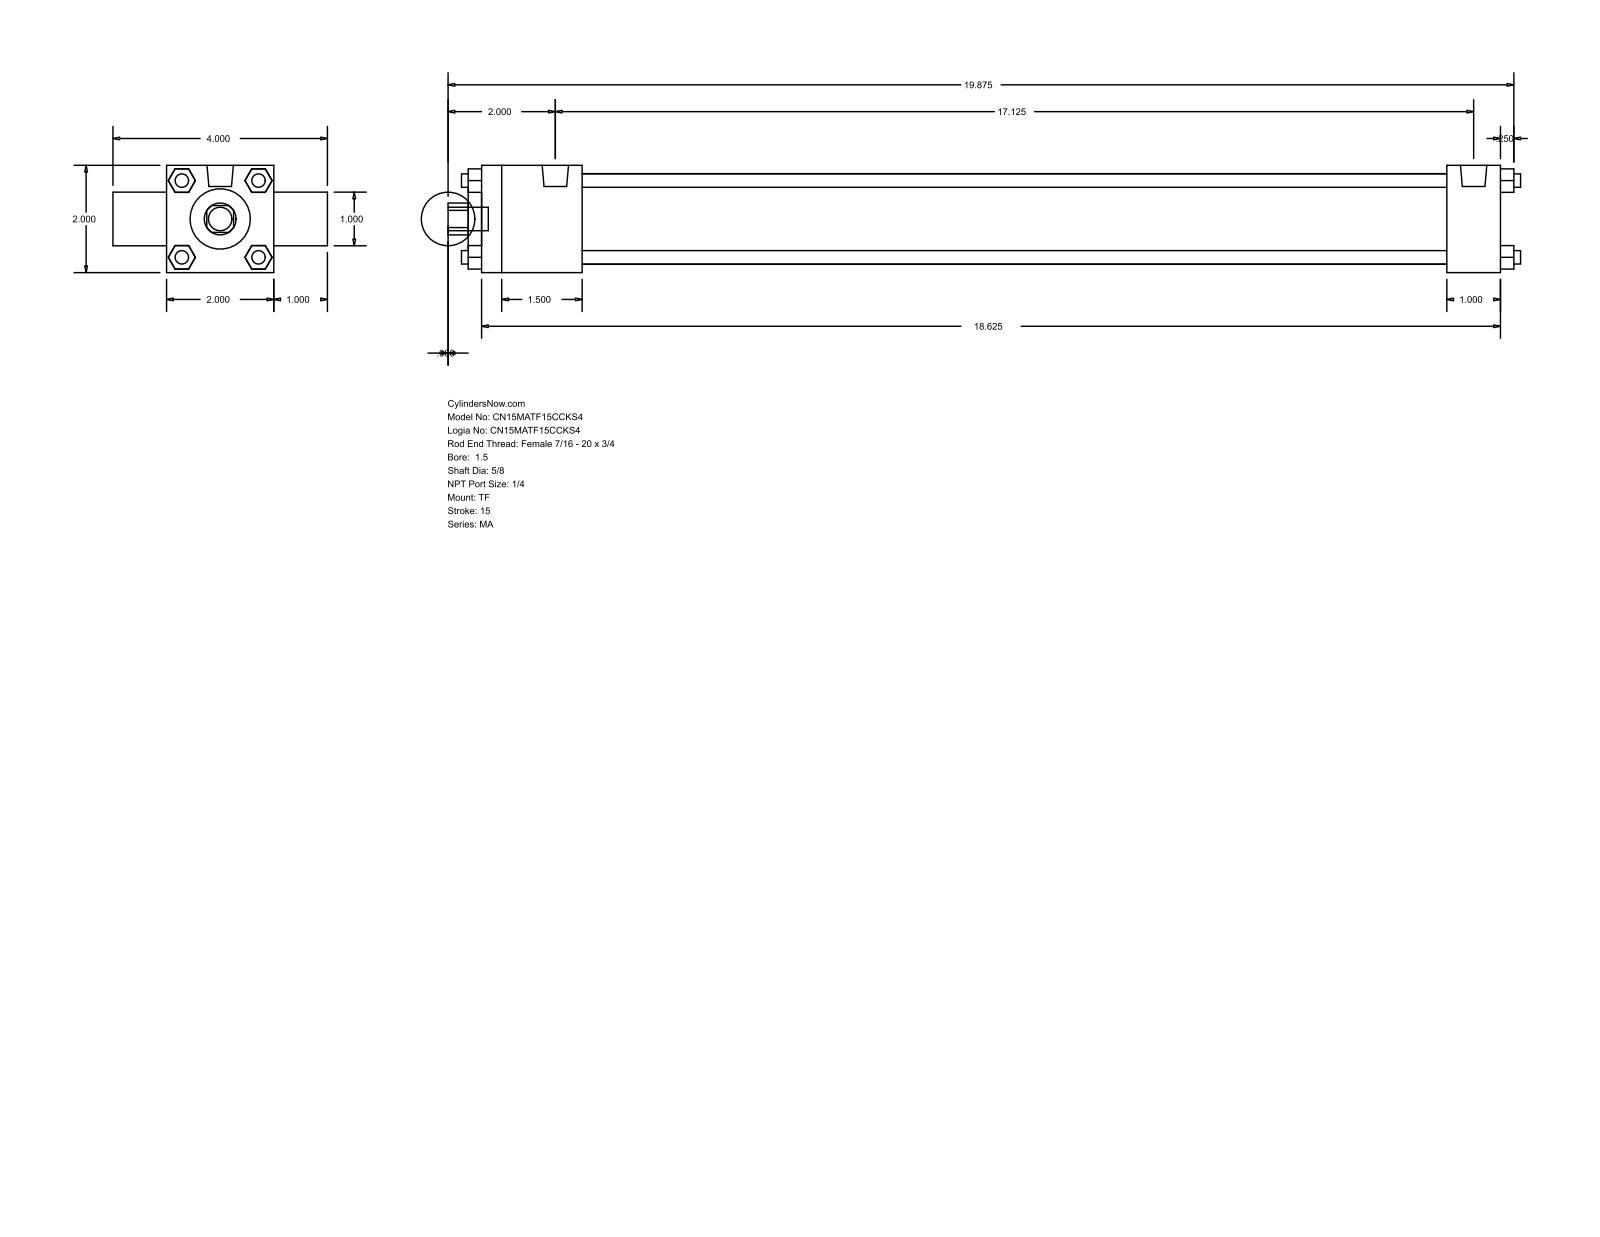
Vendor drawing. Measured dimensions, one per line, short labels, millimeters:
name: MA_TF__0150_0.625
written by: GSSL Pune (CONFIG_CONTROL_DESIGN)
unit: mm
bodies: 0 solids, 120 faces (92 planar, 28 cylindrical, 0 other)
size: 508 × 101.6 × 50.8
holes: 1× ⌀15.88, 1× ⌀25.4, 1× ⌀28.57, 1× ⌀42.93
bosses: 4× ⌀6.35, 3× ⌀7.94, 2× ⌀12.49, 1× ⌀11.11
rounds: 1× R7.54
face distances: 50.8, 482.6, 25.4, 76.2, 47.62, 457.19, 409.57, 434.98, 25.41, 488.95
